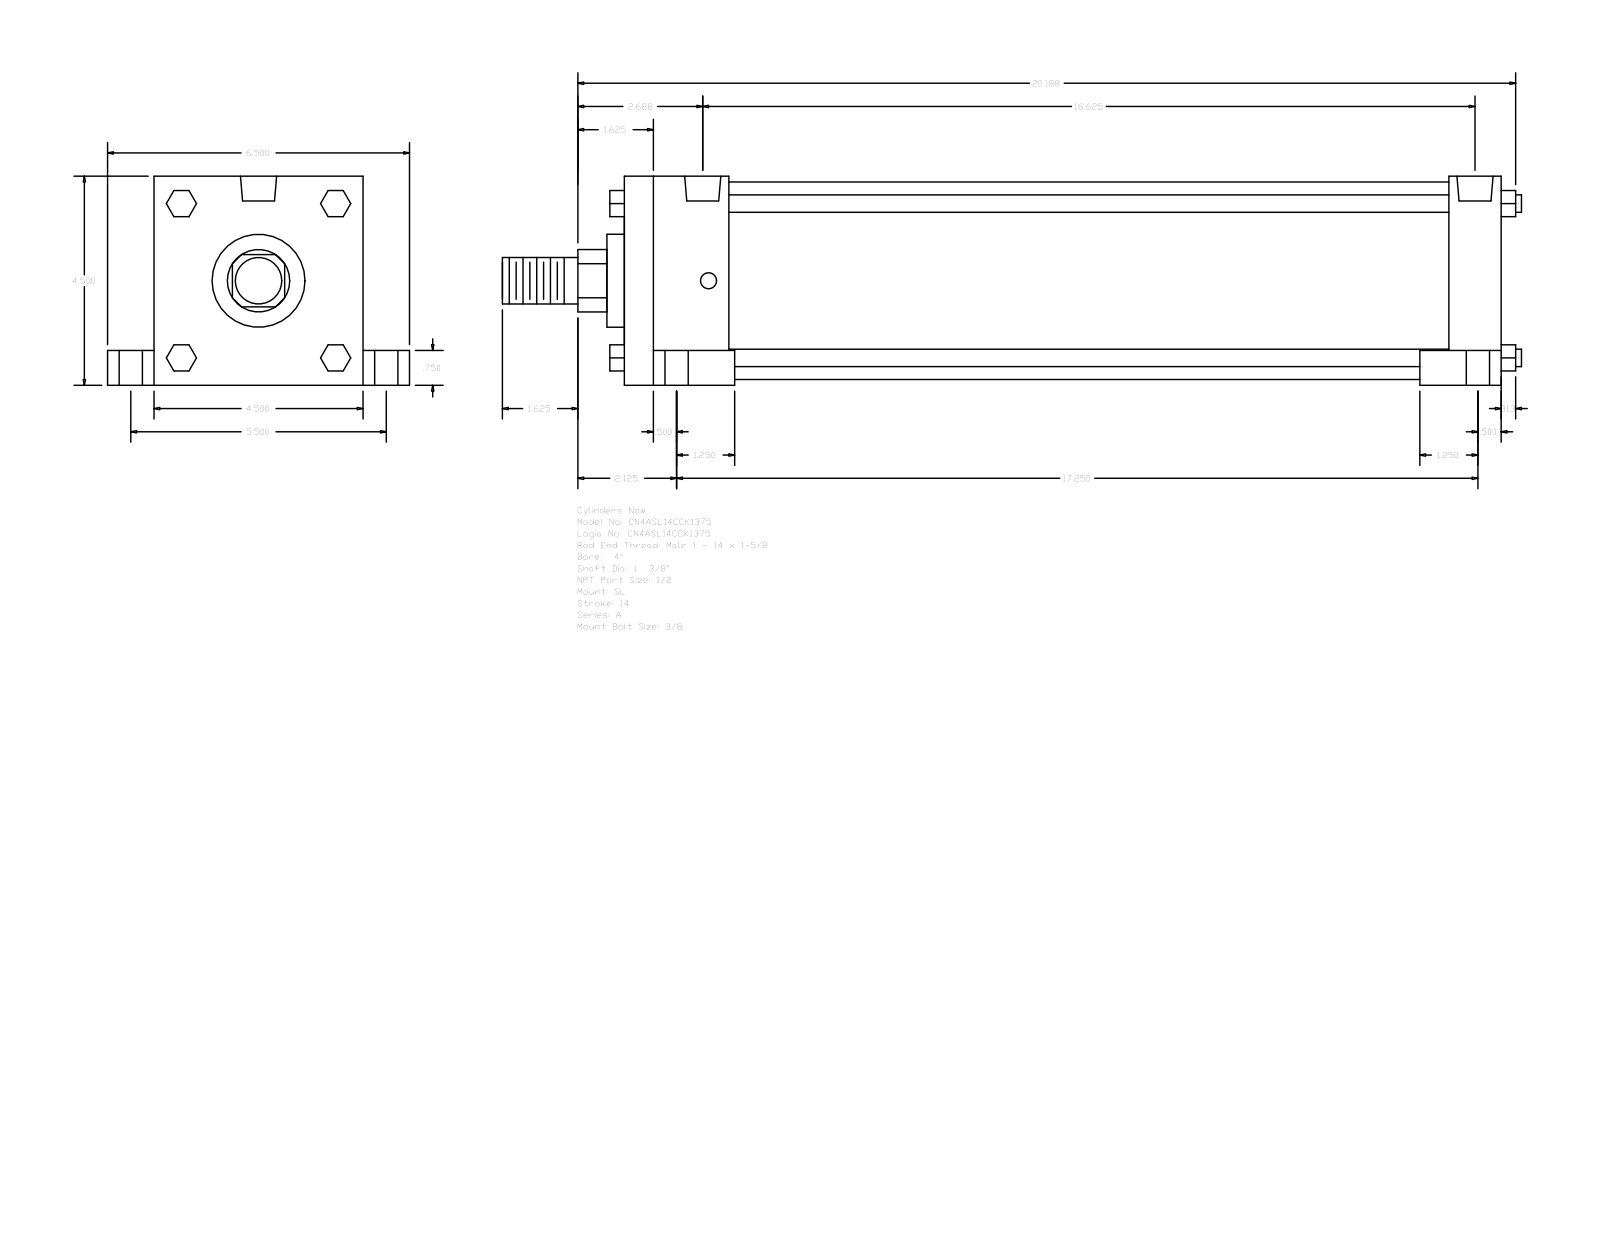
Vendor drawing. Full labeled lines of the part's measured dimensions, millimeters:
Part name (STEP PRODUCT): A_SL__0400_1.375
STEP written by: GSSL Pune (CONFIG_CONTROL_DESIGN)
Units: millimetres
Bodies: 0 solids, 150 faces (114 planar, 36 cylindrical, 0 other)
Overall size (bounding box): 557.21 × 165.1 × 114.3
Round holes (diameter × count): ⌀8.73 ×4, ⌀12.7 ×4, ⌀19.05 ×4, ⌀19.77 ×2
Round bosses / shafts (diameter × count): ⌀9.53 ×4, ⌀107.95 ×1, ⌀50.8 ×1, ⌀34.92 ×1, ⌀25.4 ×1
Partial cylindrical surfaces — rounded edges, fillets, slot ends (radius × count): R17.06 ×1
Main face-to-face distances: 114.3, 479.42, 57.15, 28.57, 25.4, 422.27, 450.85, 393.7, 139.7, 19.05
Hole centre spacings: 3.18, 69.87, 70.01, 71.29, 72, 139.7, 415.92, 419.1
